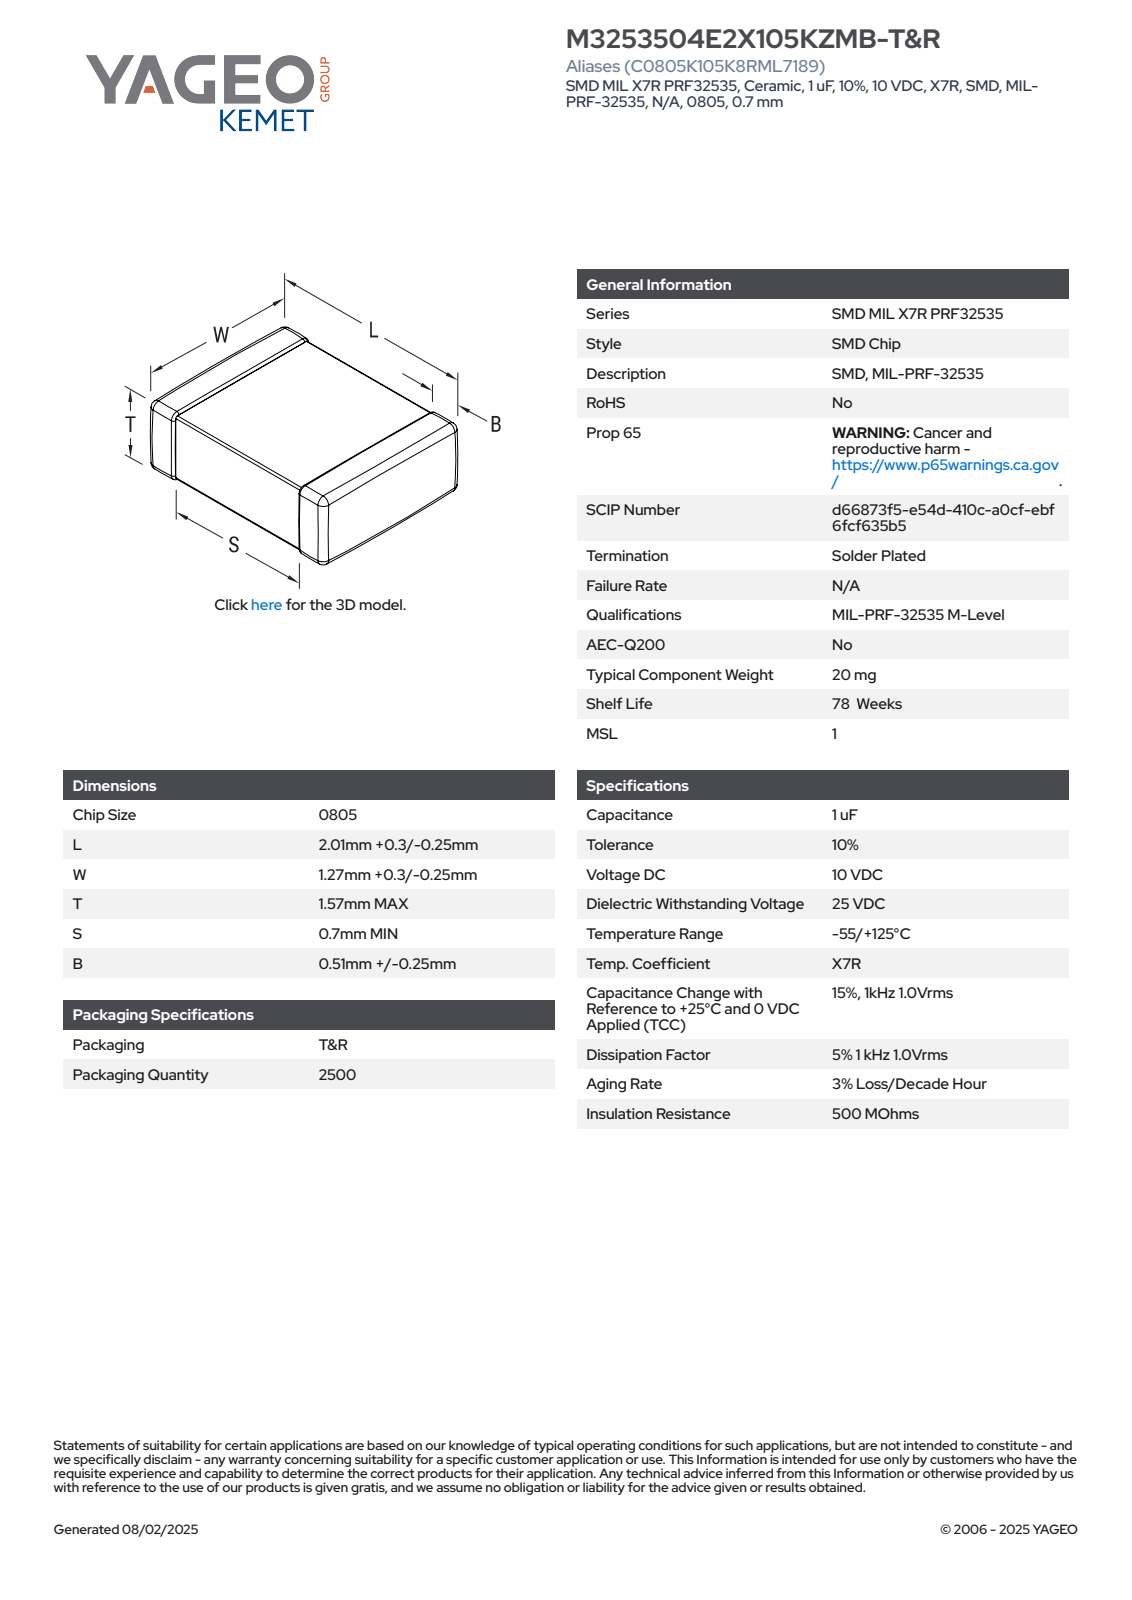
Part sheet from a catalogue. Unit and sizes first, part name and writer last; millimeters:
Units: millimetres
Overall size (bounding box): 2.31 × 1.57 × 1.57
Main face-to-face distances: 1.54, 1.57, 1.51, 2.31, 1.06, 1.25, 1.02, 1.29, 0.32, 0.38
Volume: 6 mm³ · Surface area: 20 mm²
Bodies: 4 solids, 121 faces (71 planar, 34 cylindrical, 16 other)
Part name (STEP PRODUCT): CCSM_STD_0805_L0.3W0.3T1.57S1.57B0.76
STEP written by: SolidWorks 2021 (AUTOMOTIVE_DESIGN)
